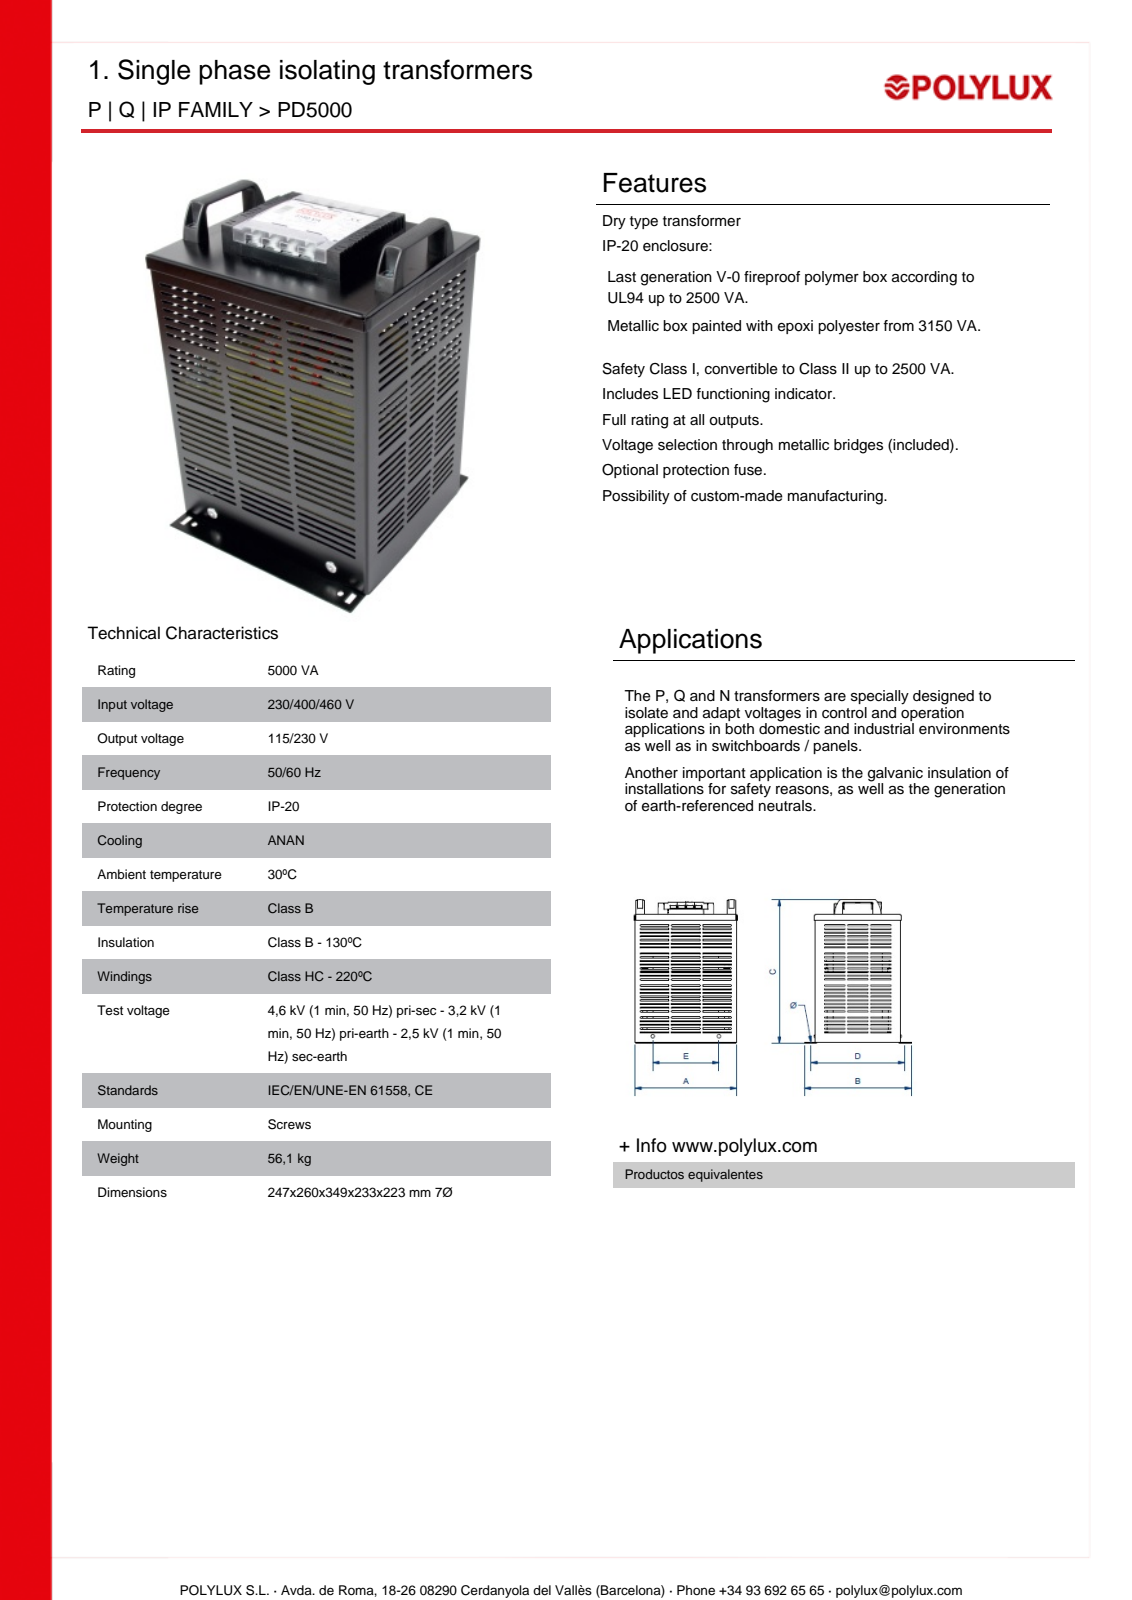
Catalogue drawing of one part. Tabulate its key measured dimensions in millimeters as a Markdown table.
| quantity | value |
| --- | --- |
| part name | RC80 |
| STEP written by | Autodesk Inventor 2018 (AUTOMOTIVE_DESIGN) |
| units | millimeters |
| bodies | 0 solids, 2900 faces (2453 planar, 100 cylindrical, 347 other) |
| overall size | 348 × 260 × 252 |
| round bosses / shafts (diameter × count) | 8 × 5, 15 × 4, 11 × 4, 6 × 4 |
| partial cylindrical surfaces (radius × count) | 2 × 8, 0.5 × 7, 0.2 × 6, 7 × 4, 820 × 3, 1 × 1, 1.25 × 1, 1.7 × 1 |
| main face-to-face distances | 2, 1.5, 3.5, 205.5, 202, 245.5, 203.5, 289, 200, 160 |
